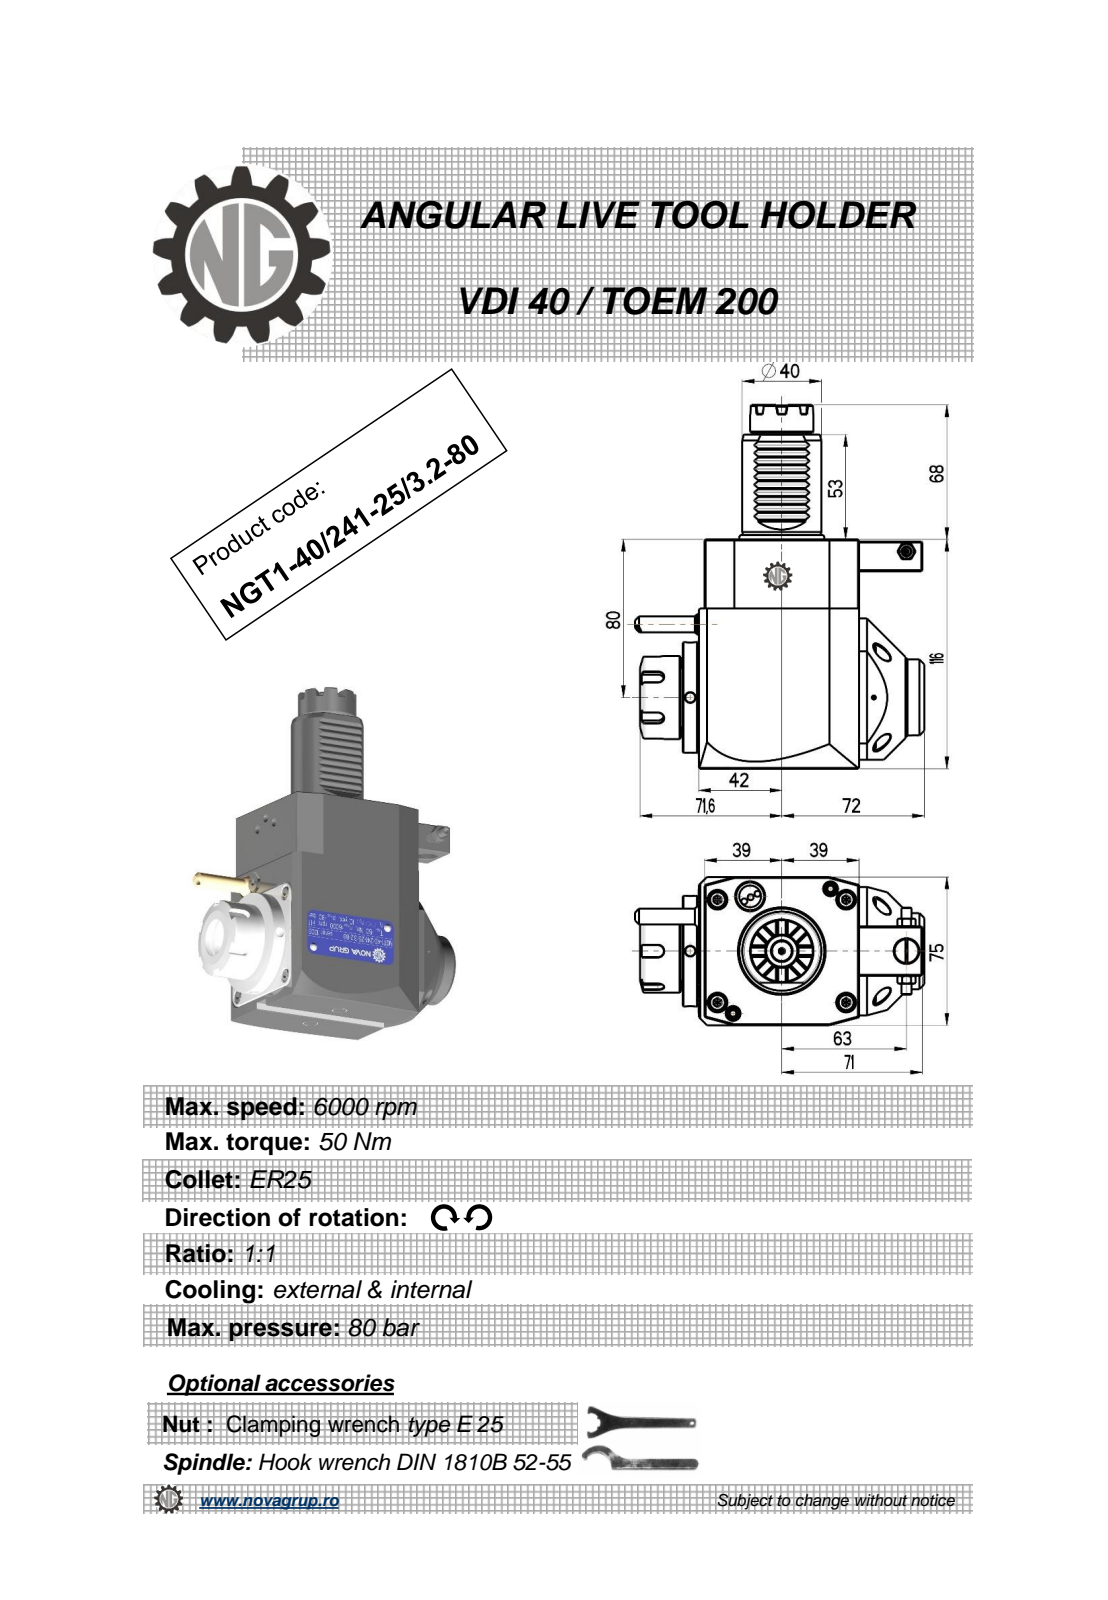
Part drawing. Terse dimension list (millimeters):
name: NGT1_40_241_25_3_2_80
written by: PRO/ENGINEER BY PARAMETRIC TECHNOLOGY CORPORATION, 2010280 (CONFIG_CONTROL_DESIGN)
unit: mm
bodies: 1 solid, 510 faces (229 planar, 91 cylindrical, 190 other)
size: 184 × 146.14 × 75
volume: 893 266 mm³; area: 73 209 mm²
holes: 3× ⌀5, 1× ⌀3, 1× ⌀4.2, 1× ⌀4.5, 1× ⌀9.5, 1× ⌀12, 1× ⌀20.3
bosses: 1× ⌀56, 1× ⌀43, 1× ⌀42, 1× ⌀40, 1× ⌀38.5, 1× ⌀33, 1× ⌀32, 1× ⌀17.2
rounds: 12× R0.26, 10× R0.3, 6× R0.2, 5× R3, 1× R0.5, 1× R40
face distances: 75, 116, 81, 78, 3, 11, 89, 8, 2.8, 80.8
hole spacings: 39.49, 40.93, 72.4, 109.25, 131.9
